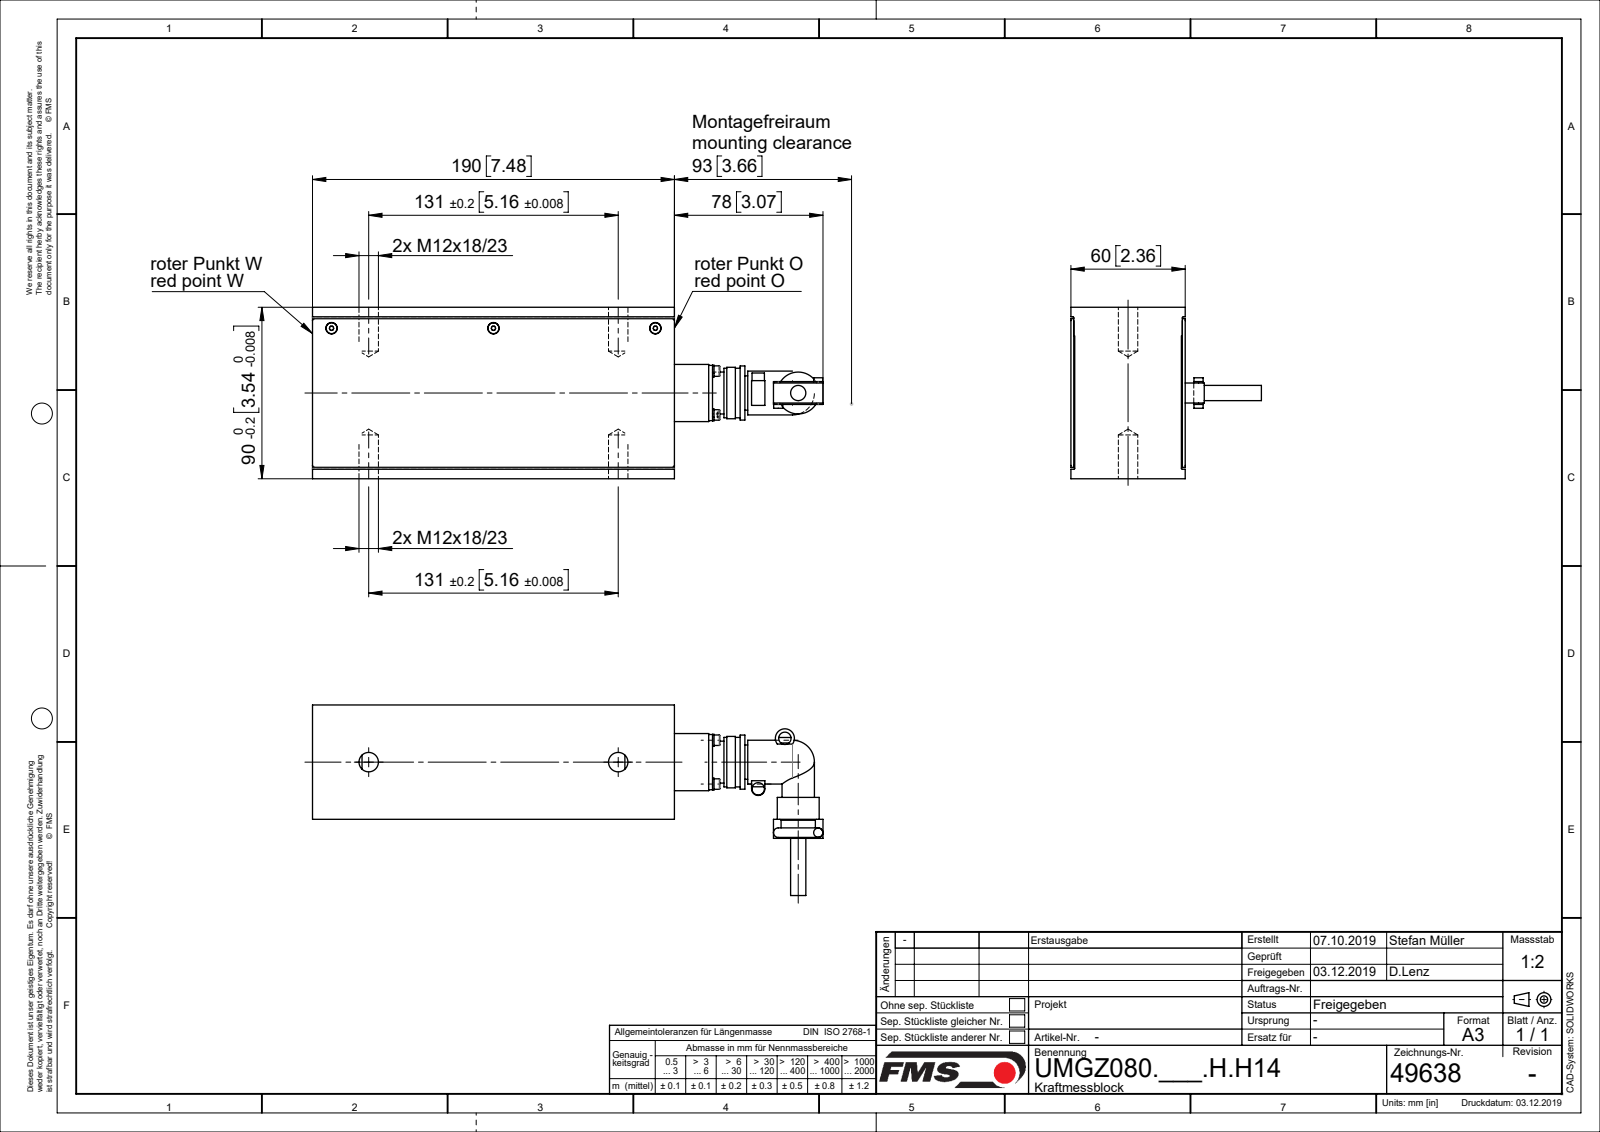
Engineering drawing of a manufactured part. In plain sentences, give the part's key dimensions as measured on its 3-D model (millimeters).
The part is named "U49638; U4963504; U49541; L49026 (+6 more)". Its 3-D file was written by "Mechanical Desktop 2007 (CONFIG_CONTROL_DESIGN)". It is 19 solids with 399 faces: 156 planar, 160 cylindrical and 83 other. Overall it measures 268 by 100 by 90 millimeters. Its volume is 1 043 000 cubic millimeters and its surface area 152 172 square millimeters. Round holes: 7 of diameter 2.6, 4 of diameter 3.2, 4 of diameter 3.4, 4 of diameter 3.5, 3 of diameter 6, 2 of diameter 10.44, 1 of diameter 23. Round bosses or shafts: 7 of diameter 3, 4 of diameter 6.2, 4 of diameter 5.5, 2 of diameter 22, 2 of diameter 6.5, 2 of diameter 4.8, 1 of diameter 28.4, 1 of diameter 27. Partial cylindrical surfaces (rounded edges, fillets, slot ends): 4 of radius 1, 2 of radius 2.5, 1 of radius 3.5, 1 of radius 5. The main face-to-face distances are 1.5, 58.5, 2, 0.5, 58, 56.5, 60, 57, 56, 90. The hole center spacings are 16.26, 23, 32.53, 85, 131, 170.
